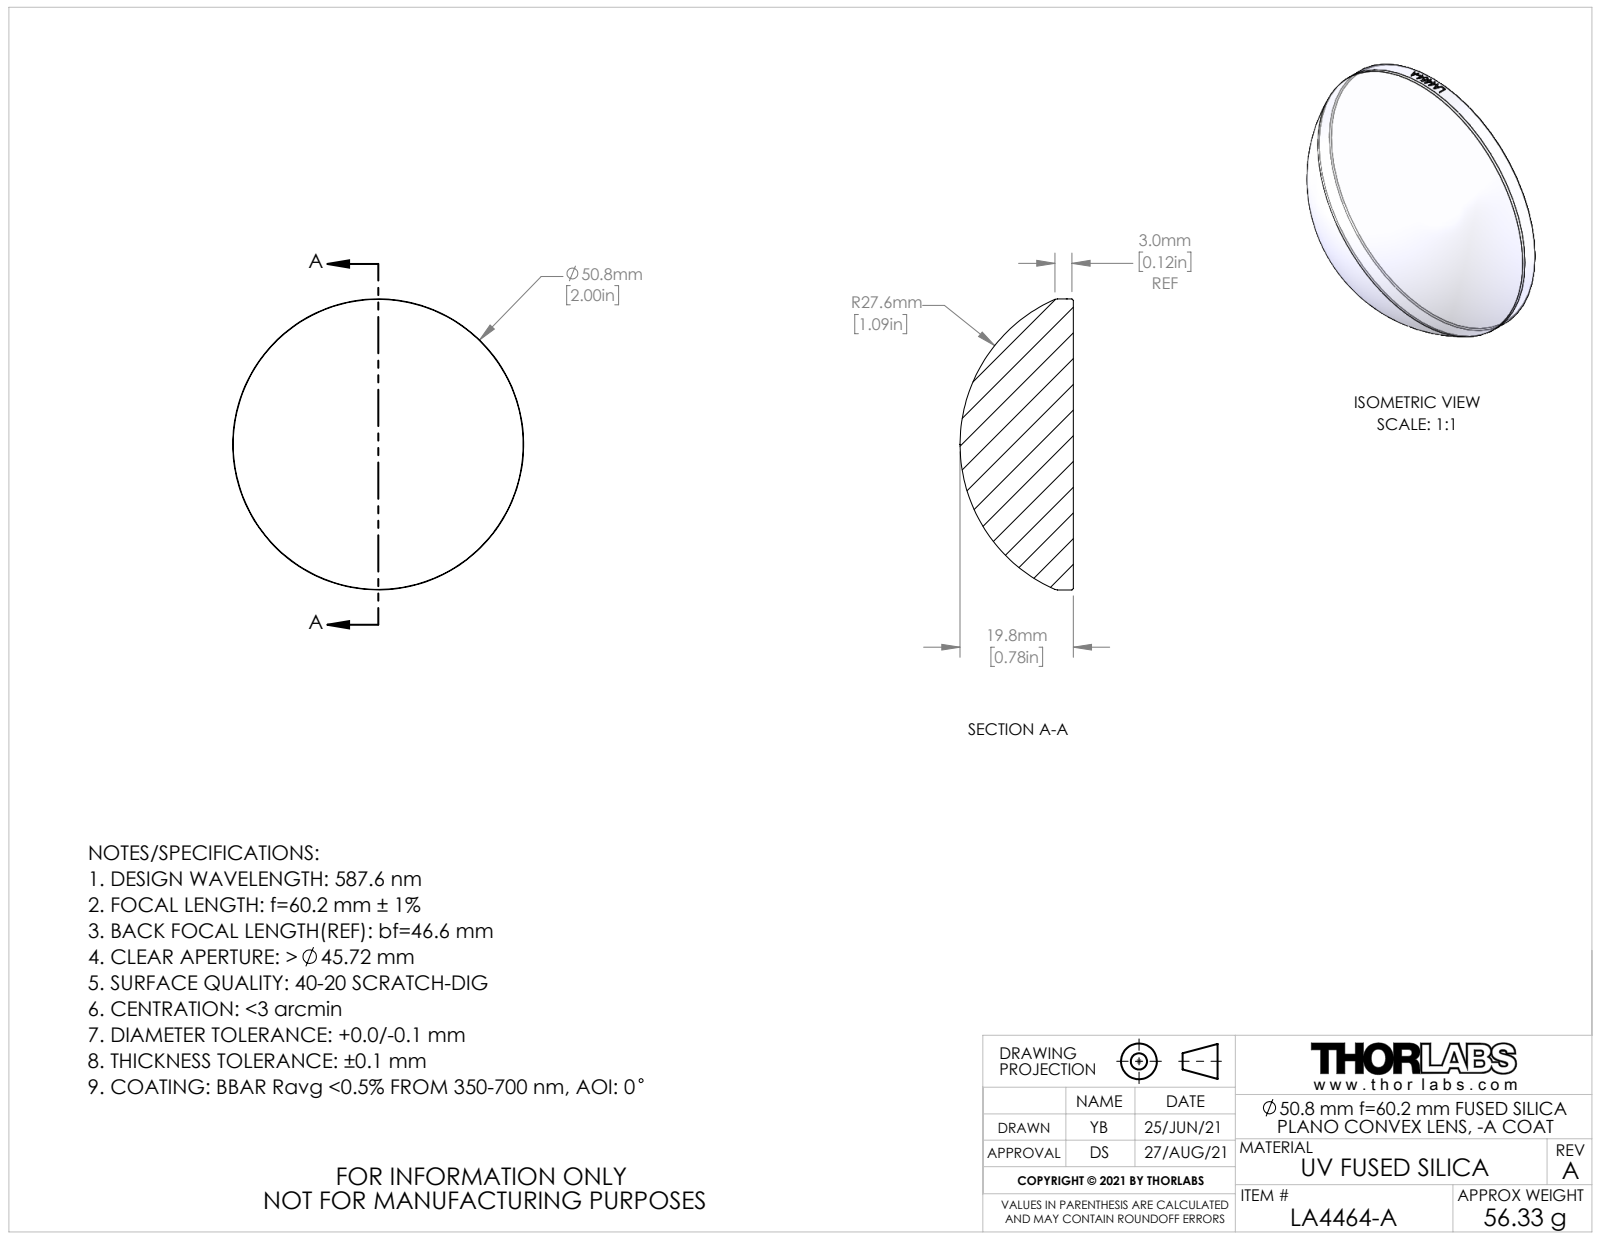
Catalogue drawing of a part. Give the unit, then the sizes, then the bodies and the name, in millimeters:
Units: millimetres
Overall size (bounding box): 50.8 × 50.8 × 19.79
Round bosses / shafts (diameter × count): ⌀50.8 ×1
Volume: 25 570 mm³ · Surface area: 5 393 mm²
Bodies: 1 solid, 23 faces (1 planar, 16 cylindrical, 6 other)
Part name (STEP PRODUCT): CTN017563; CTN017535-E0W
STEP written by: SolidWorks 2018 (AUTOMOTIVE_DESIGN)
